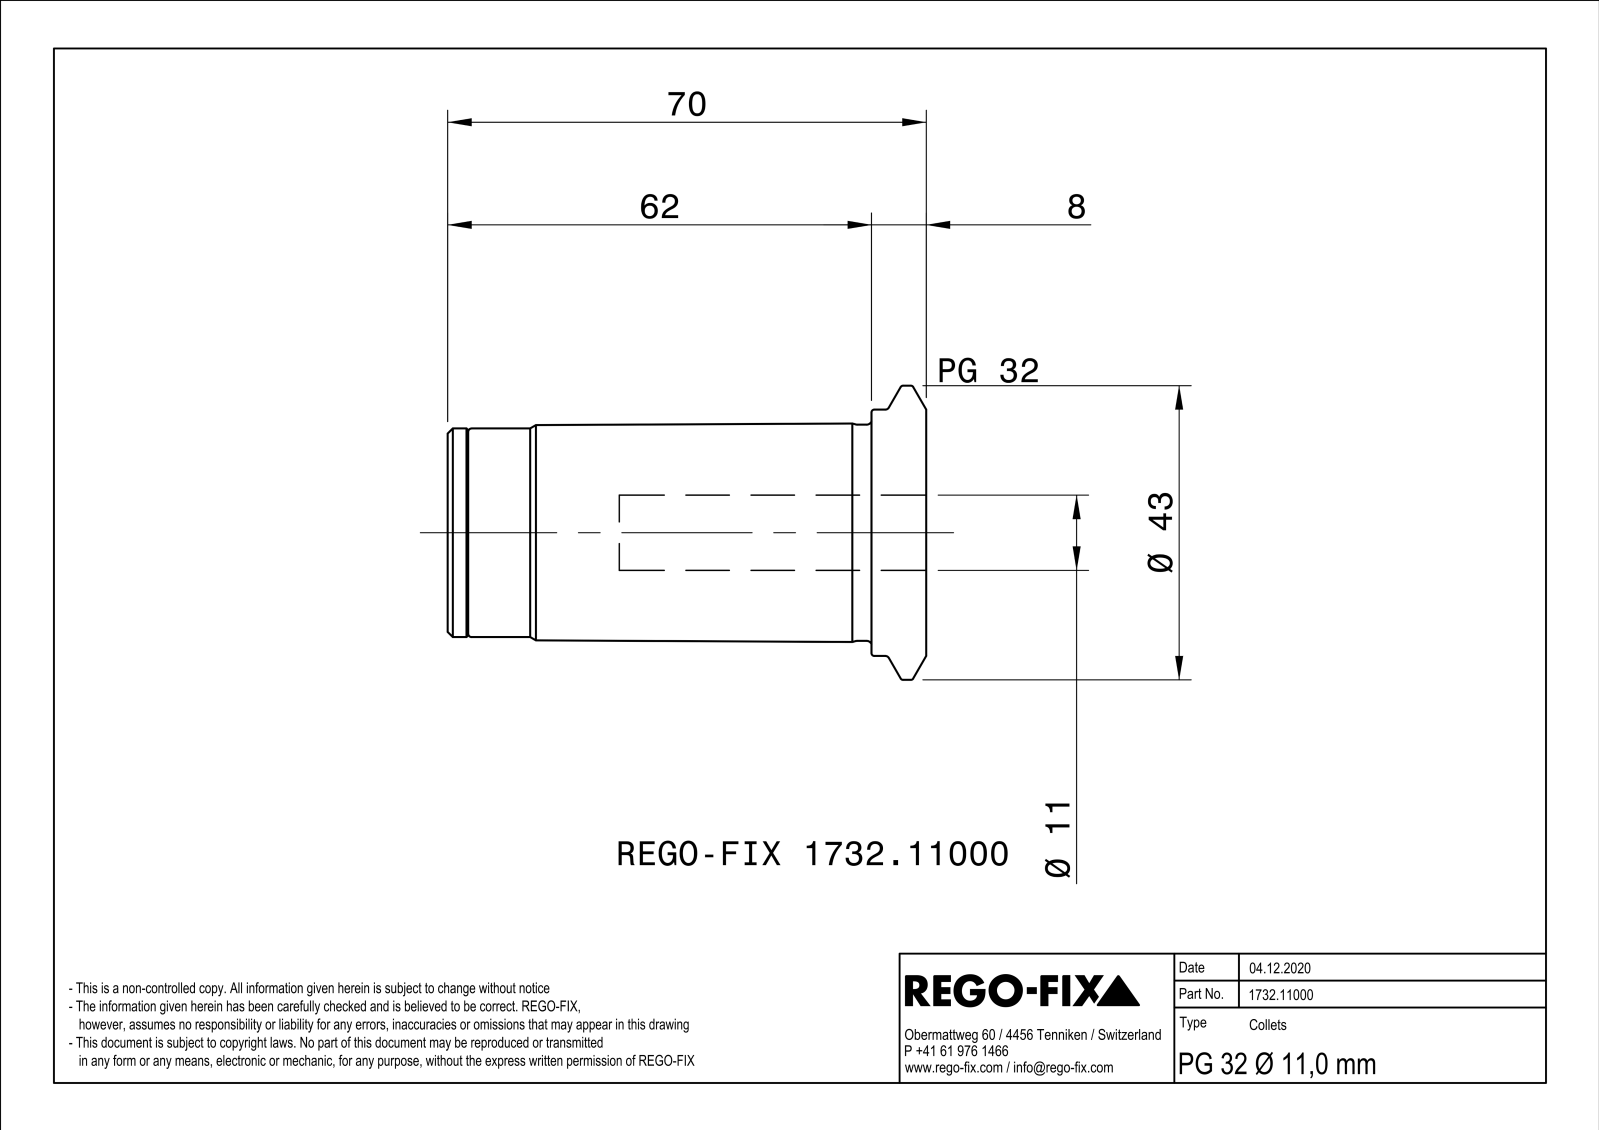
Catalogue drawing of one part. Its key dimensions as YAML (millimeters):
part_name: "NOCUT"
step_written_by: "SIEMENS PLM Software Solid Edge ST10 (AUTOMOTIVE_DESIGN)"
units: millimeters
bodies: {solids: 1, faces: 127, planar: 31, cylindrical: 41, other: 55}
overall_size: [70, 43, 42.99]
volume: 46200
surface_area: 16588
round_holes:
  - {diameter: 4, count: 3}
  - {diameter: 8.92, count: 1}
  - {diameter: 10.5, count: 1}
  - {diameter: 11, count: 1}
  - {diameter: 15.5, count: 1}
  - {diameter: 26.92, count: 1}
  - {diameter: 28.5, count: 1}
round_bosses_or_shafts:
  - {diameter: 43, count: 1}
  - {diameter: 36, count: 1}
  - {diameter: 31.6, count: 1}
  - {diameter: 30.5, count: 1}
  - {diameter: 26.5, count: 1}
  - {diameter: 21, count: 1}
partial_cylinders:
  - {radius: 2, count: 6}
  - {radius: 3.5, count: 3}
  - {radius: 3.98, count: 1}
  - {radius: 4.75, count: 1}
  - {radius: 8.75, count: 1}
face_to_face_distances: [1, 70, 58, 12, 59, 11, 8, 60, 2, 10]
hole_center_spacings: [7.75, 13.42, 13.43]
